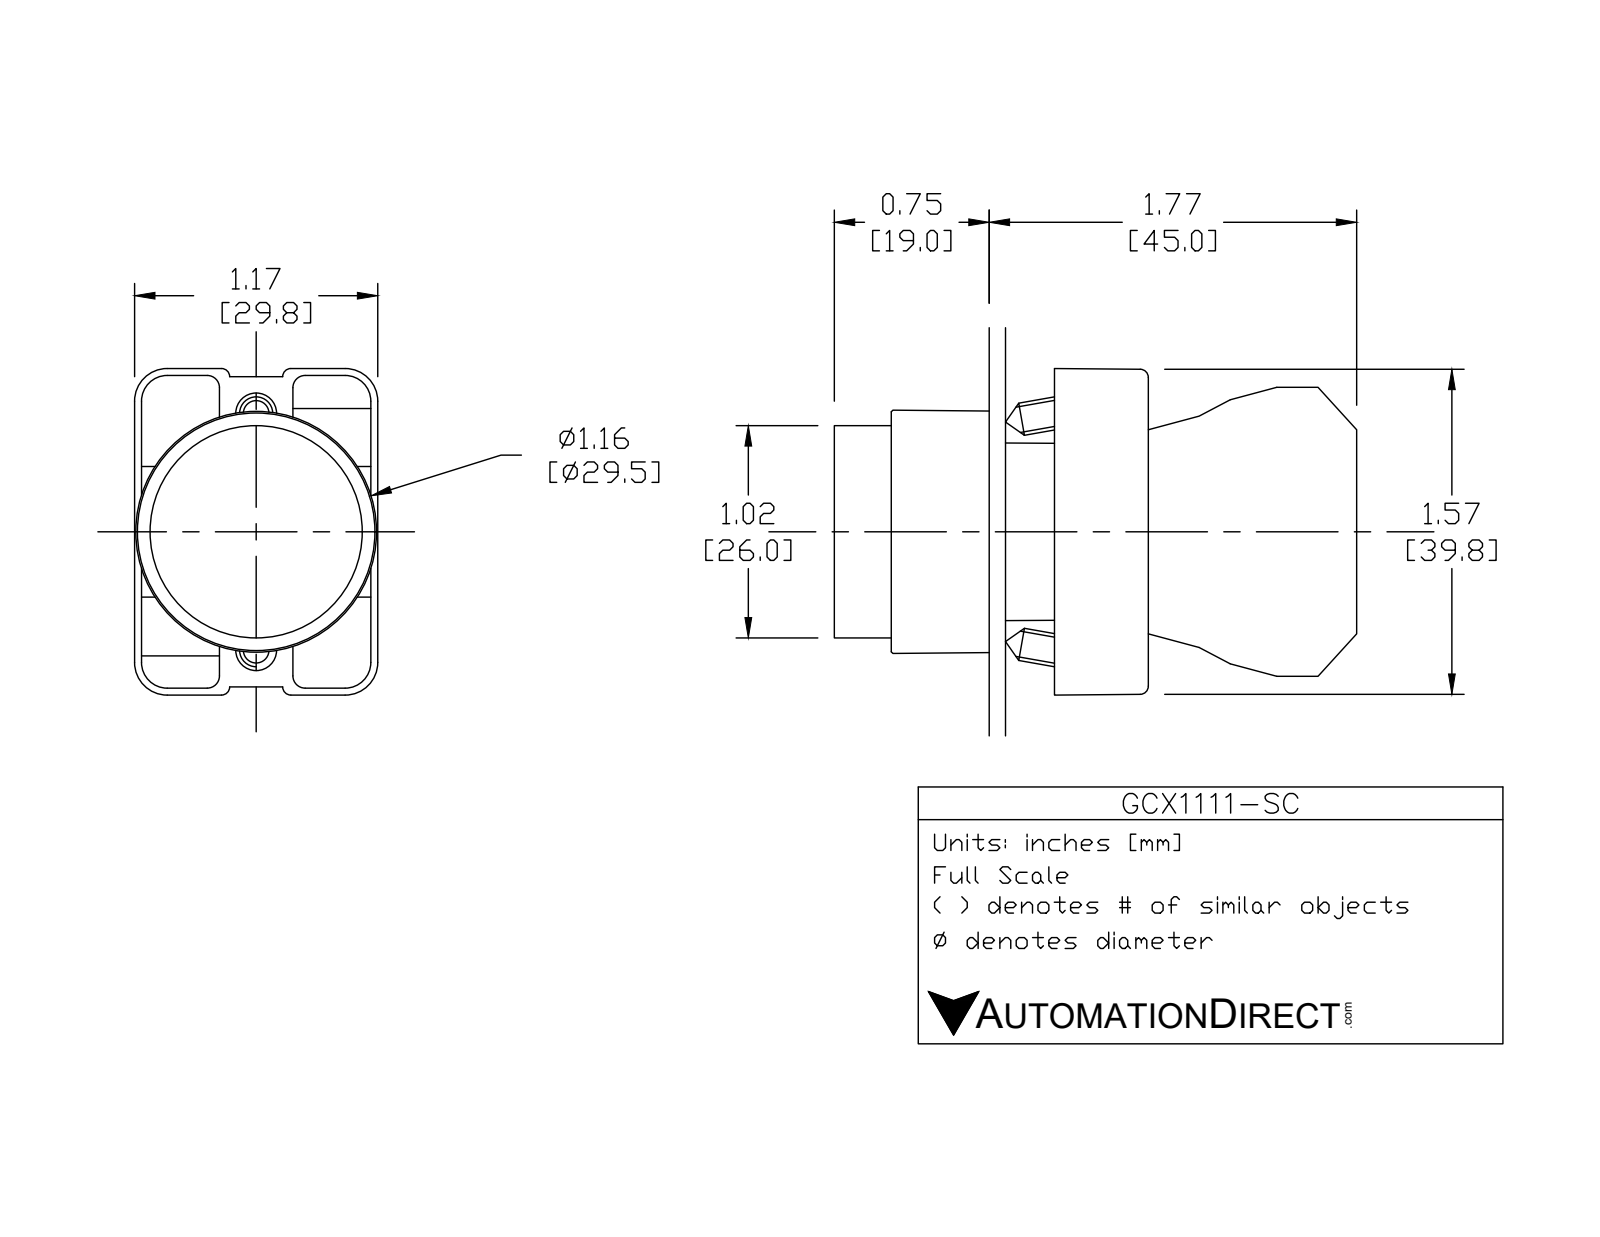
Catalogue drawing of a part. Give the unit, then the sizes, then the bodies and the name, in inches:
Units: inches
Overall size (bounding box): 1.683 × 1.581 × 1.177
Round holes (diameter × count): ⌀0.124 ×2, ⌀0.13 ×2, ⌀0.197 ×1, ⌀0.878 ×1, ⌀0.888 ×1, ⌀1.024 ×1
Round bosses / shafts (diameter × count): ⌀0.157 ×2, ⌀1.175 ×1, ⌀1.004 ×1, ⌀0.945 ×1, ⌀0.856 ×1, ⌀0.78 ×1
Partial cylindrical surfaces — rounded edges, fillets, slot ends (radius × count): R0.059 ×24, R0.041 ×12, R0.124 ×12, R0.157 ×12, R0.039 ×4, R0.128 ×2, R0.392 ×1, R0.398 ×1
Main face-to-face distances: 0.033, 1.193, 0.031, 0.72, 0.472, 0.689, 1.161, 1.469, 1.437, 0.748
Volume: 0.933 in³ · Surface area: 19.73 in²
Bodies: 5 solids, 290 faces (147 planar, 118 cylindrical, 25 other)
Part name (STEP PRODUCT): ecx1029; GCX1111 OPERATOR; GCX1111-SC
STEP written by: SolidWorks 2016 (AUTOMOTIVE_DESIGN)
